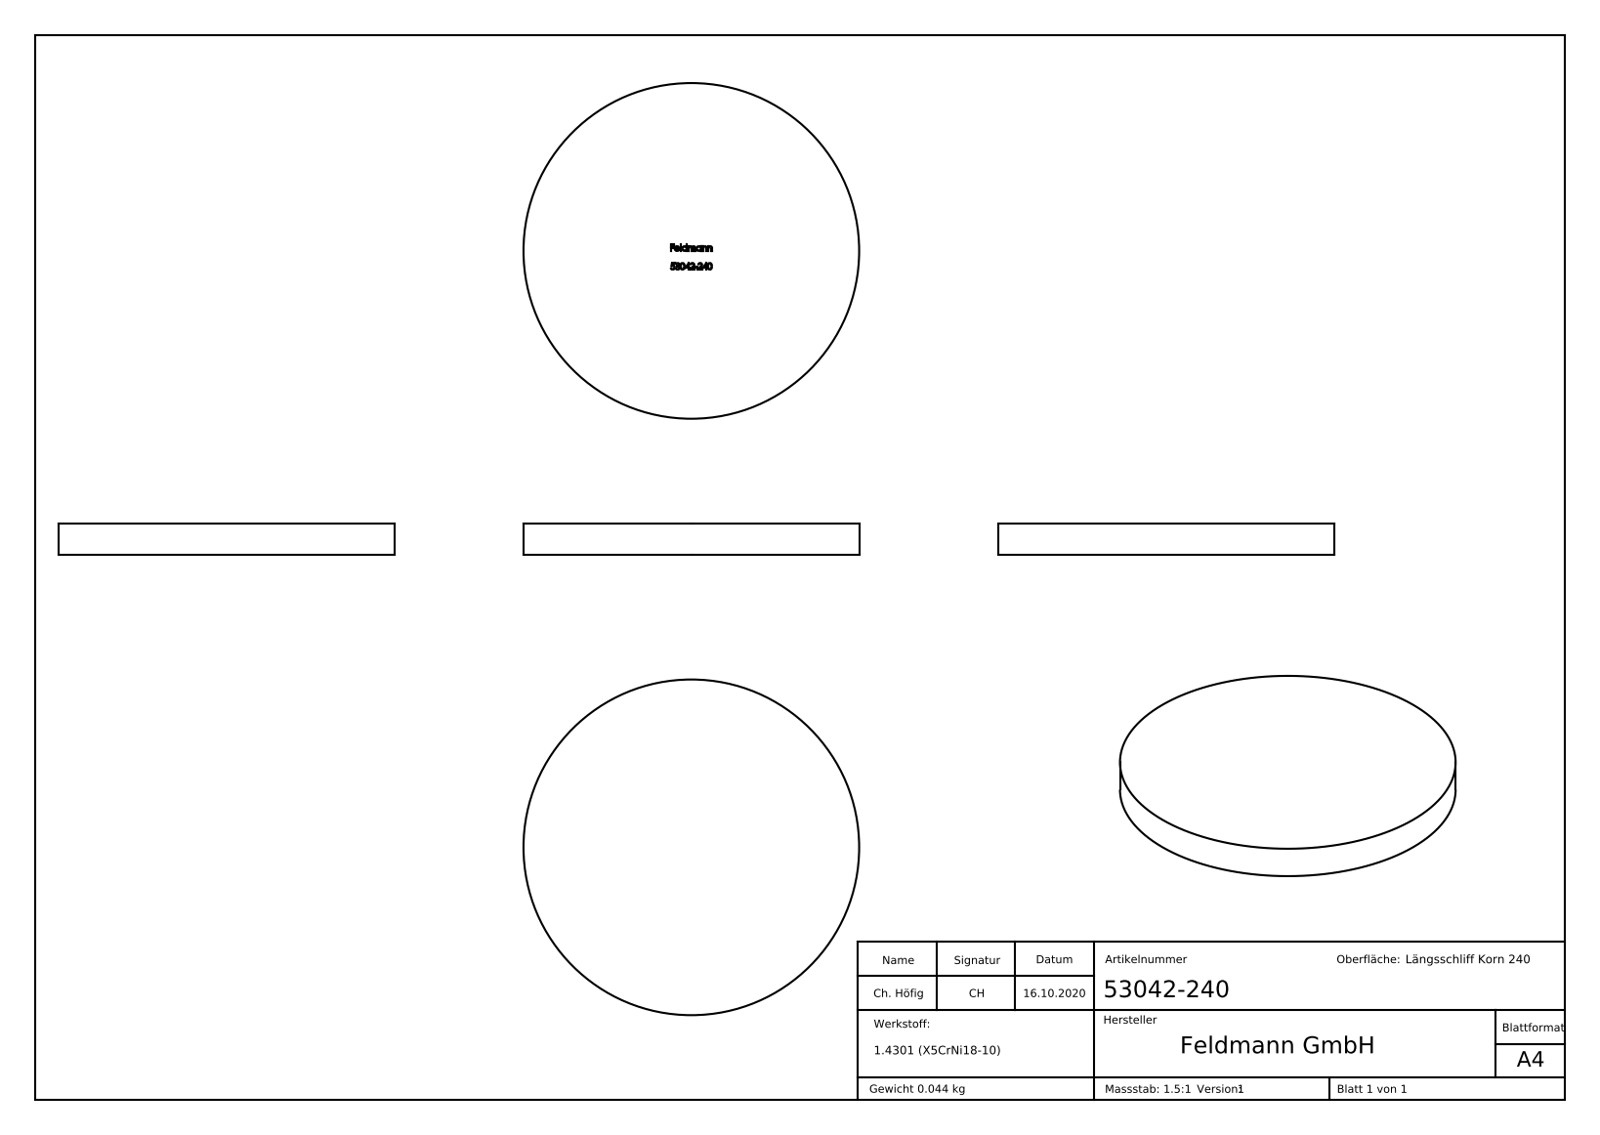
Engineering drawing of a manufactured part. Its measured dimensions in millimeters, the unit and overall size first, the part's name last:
Units: millimetres
Overall size (bounding box): 42 × 42 × 4
Round bosses / shafts (diameter × count): ⌀42 ×1
Main face-to-face distances: 4, 3.9, 2.2, 1.78, 2.18, 0.71, 0.83, 2.41, 2.25, 0.99
Volume: 5 542 mm³ · Surface area: 3 305 mm²
Bodies: 1 solid, 233 faces (131 planar, 2 cylindrical, 100 other)
Part name (STEP PRODUCT): 53042-240
STEP written by: SolidWorks 2018 (CONFIG_CONTROL_DESIGN)
